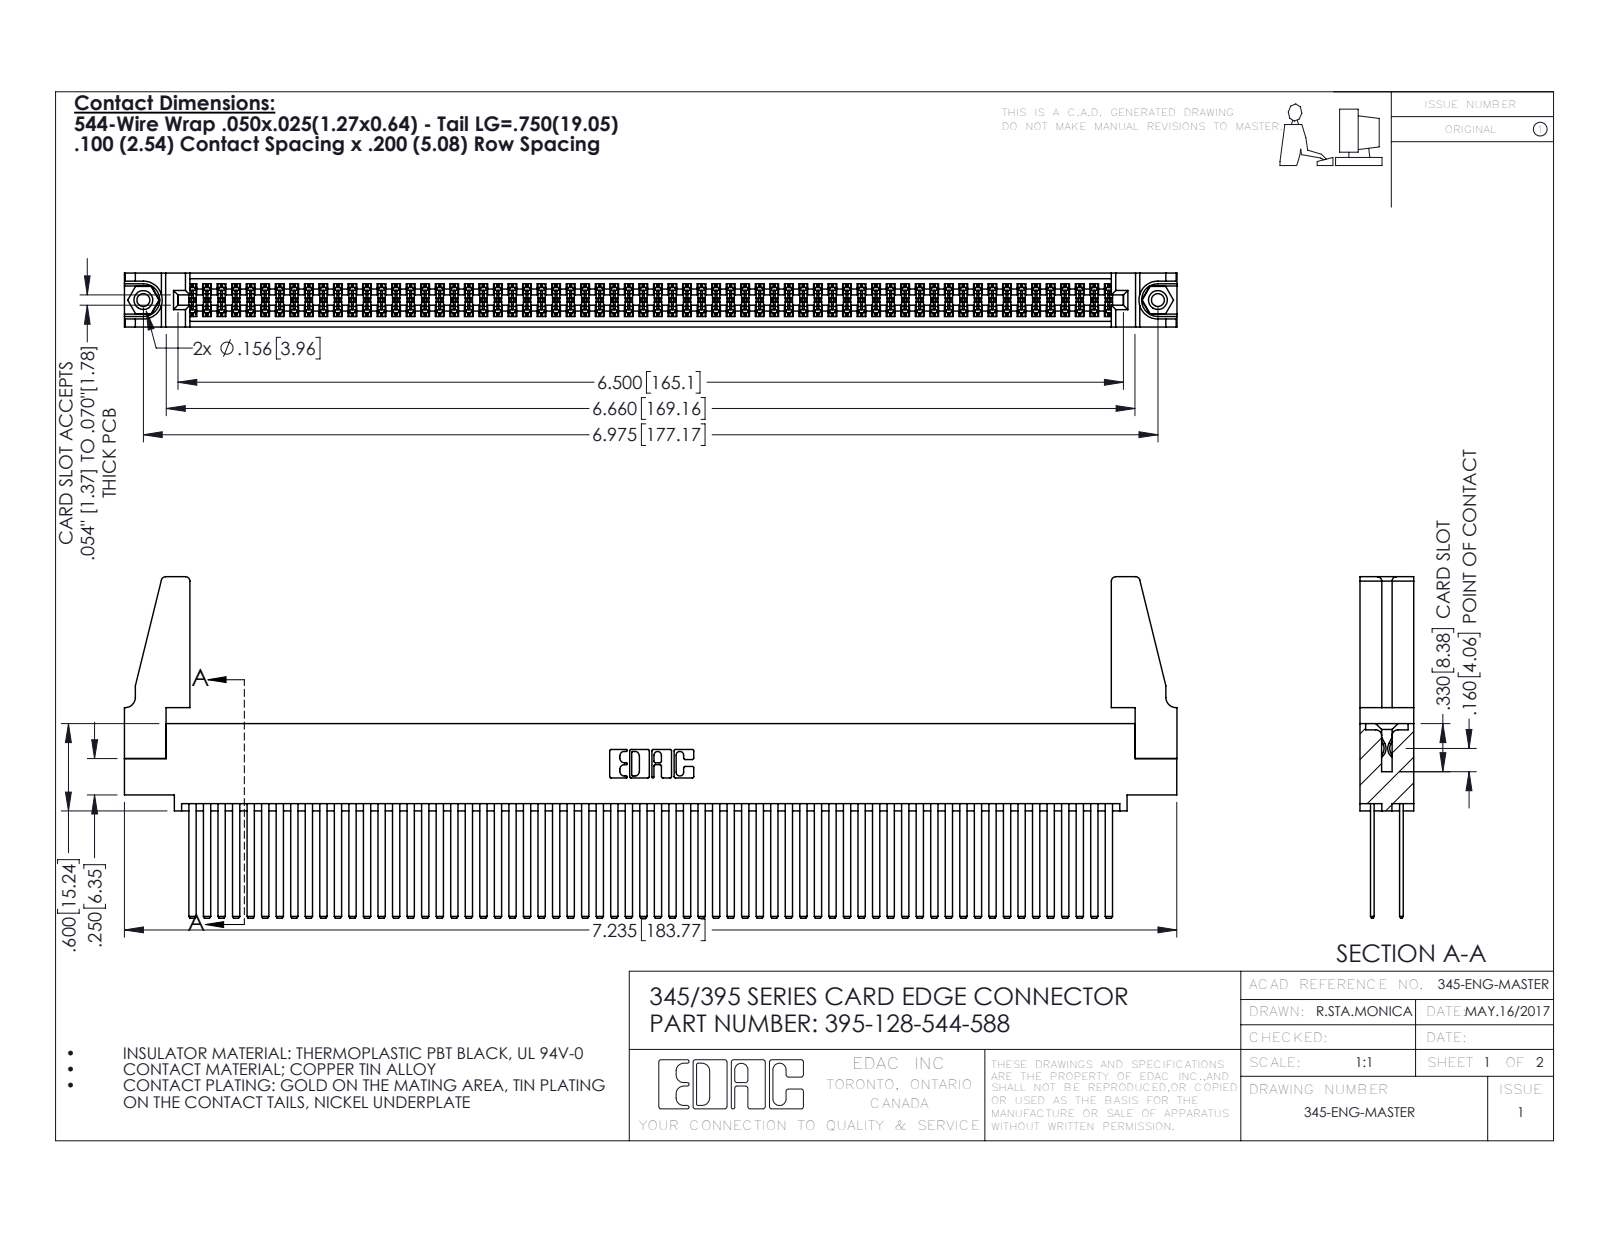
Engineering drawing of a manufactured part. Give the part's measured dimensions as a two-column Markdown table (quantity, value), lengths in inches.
| quantity | value |
| --- | --- |
| part name | 395-128-544-588; 345 Part_0.110 Offset - 0.156 Dia-TH; 345-250-001_345-250-001-102; 345-292-001_345-293-144 (+1 more) |
| STEP written by | SolidWorks 2016 (CONFIG_CONTROL_DESIGN) |
| units | inches |
| bodies | 133 solids, 5886 faces (3868 planar, 2002 cylindrical, 16 other) |
| overall size | 7.236 × 2.347 × 0.37 |
| volume | 1.405 in³ |
| surface area | 59.11 in² |
| round holes (diameter × count) | 0.089 × 2, 0.125 × 2, 0.156 × 2, 0.064 × 1 |
| round bosses / shafts (diameter × count) | 0.155 × 2 |
| partial cylindrical surfaces (radius × count) | 0.006 × 192, 0.01 × 22, 0.03 × 8, 0.007 × 6, 0.031 × 6, 0.026 × 3, 0.014 × 2, 0.019 × 2 |
| main face-to-face distances | 0.072, 0.298, 0.2, 0.098, 0.272, 0.025, 0.225, 0.37, 0.175, 0.149 |
| hole center spacings | 0.27, 6.739, 6.975 |
